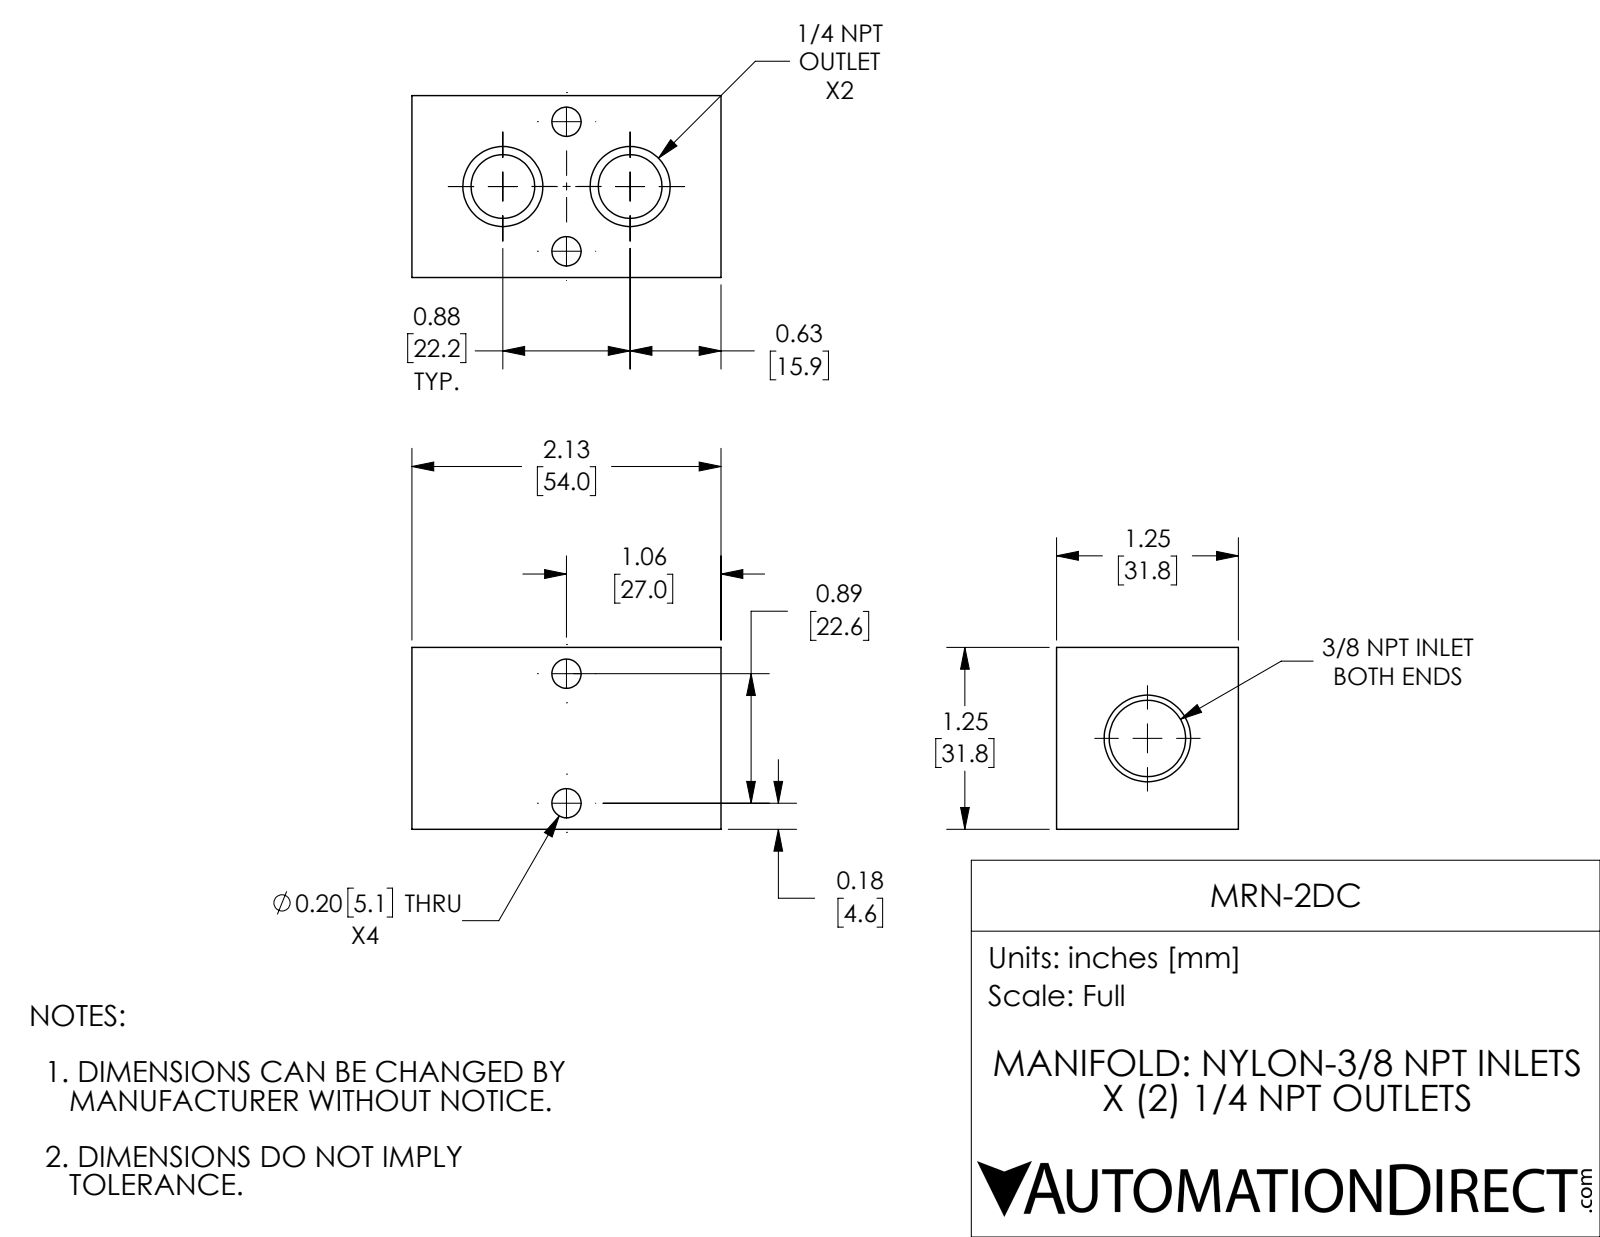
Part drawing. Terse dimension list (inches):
name: MRN-2DC
written by: SolidWorks 2018 (AUTOMOTIVE_DESIGN)
unit: in
bodies: 1 solid, 44 faces (6 planar, 30 cylindrical, 8 other)
size: 2.125 × 1.25 × 1.25
volume: 2.6 in³; area: 19.44 in²
holes: 4× ⌀0.201, 2× ⌀0.438, 1× ⌀0.525
face distances: 1.25, 2.125
hole spacings: 0.624, 0.89, 0.875
